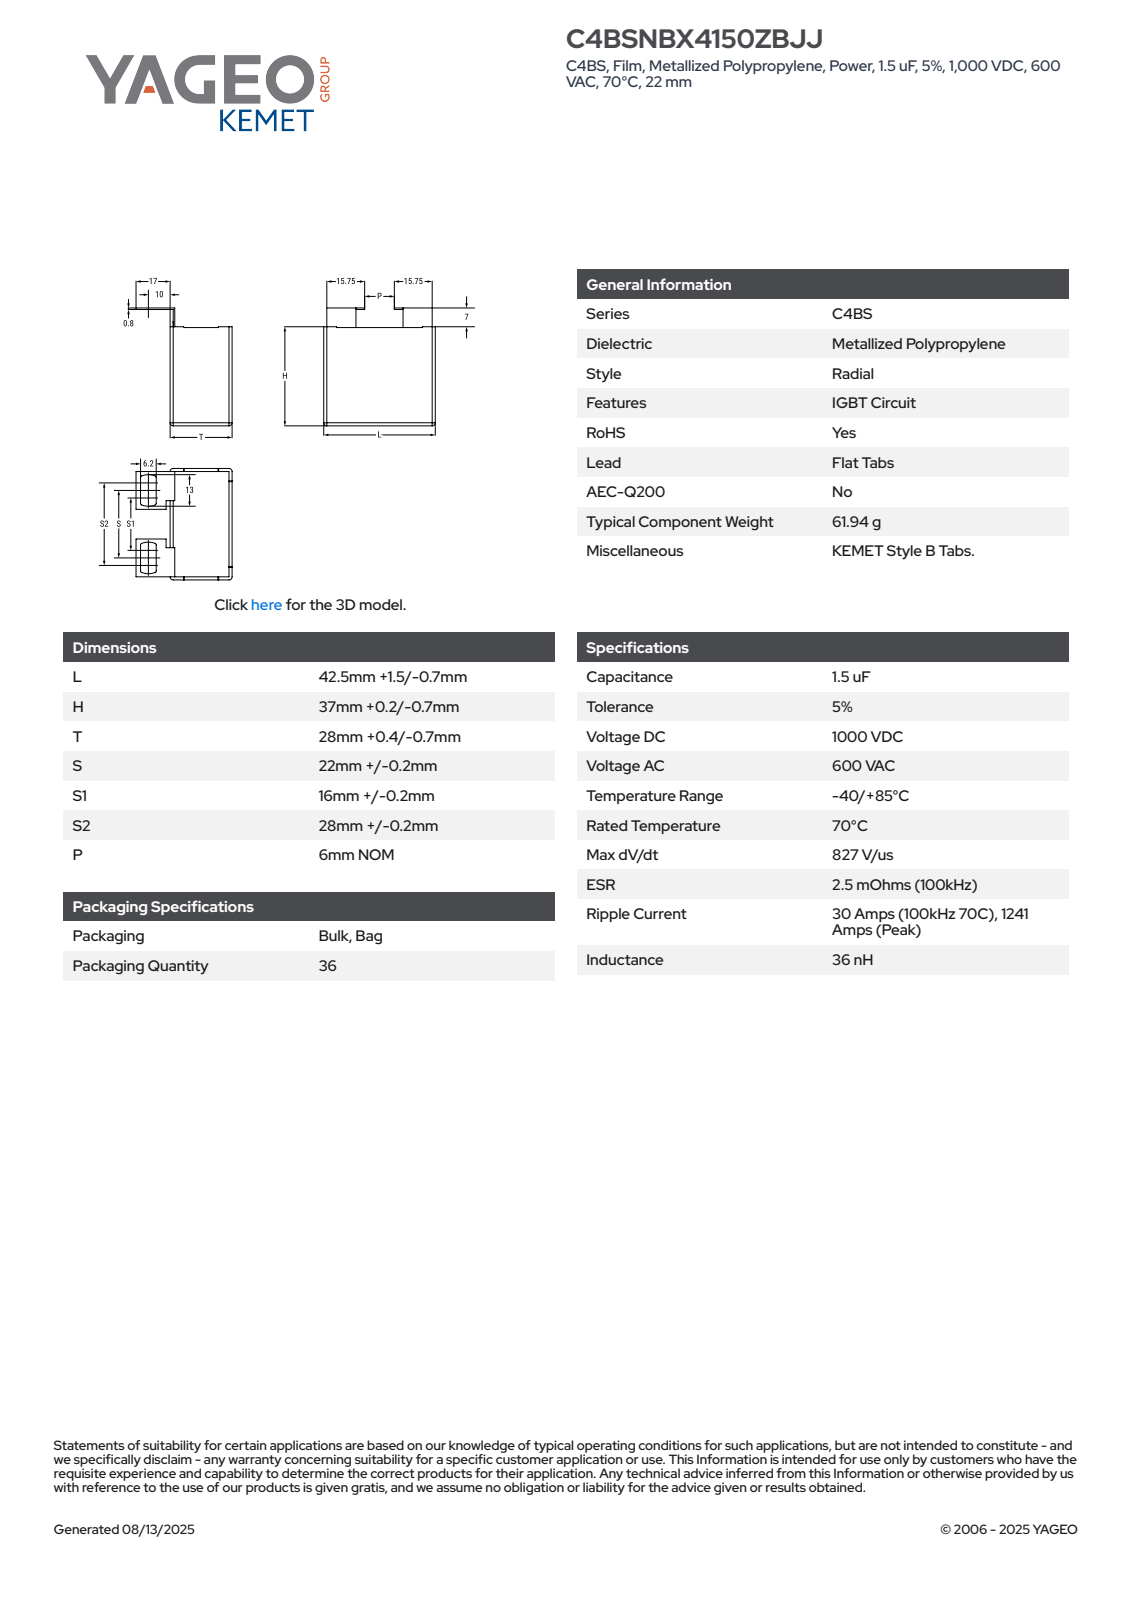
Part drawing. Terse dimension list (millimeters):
name: CFP_C4BB_42.5X37X28_L44H37.2T28.4S22.2
written by: SolidWorks 2014 (AUTOMOTIVE_DESIGN)
unit: mm
bodies: 4 solids, 93 faces (85 planar, 8 cylindrical, 0 other)
size: 45.4 × 44.2 × 44
volume: 47 020 mm³; area: 9 477 mm²
rounds: 4× R4.6, 2× R0.2
face distances: 28.4, 37.2, 44, 0.8, 7, 44.2, 6.2, 43.4, 2, 26.4
